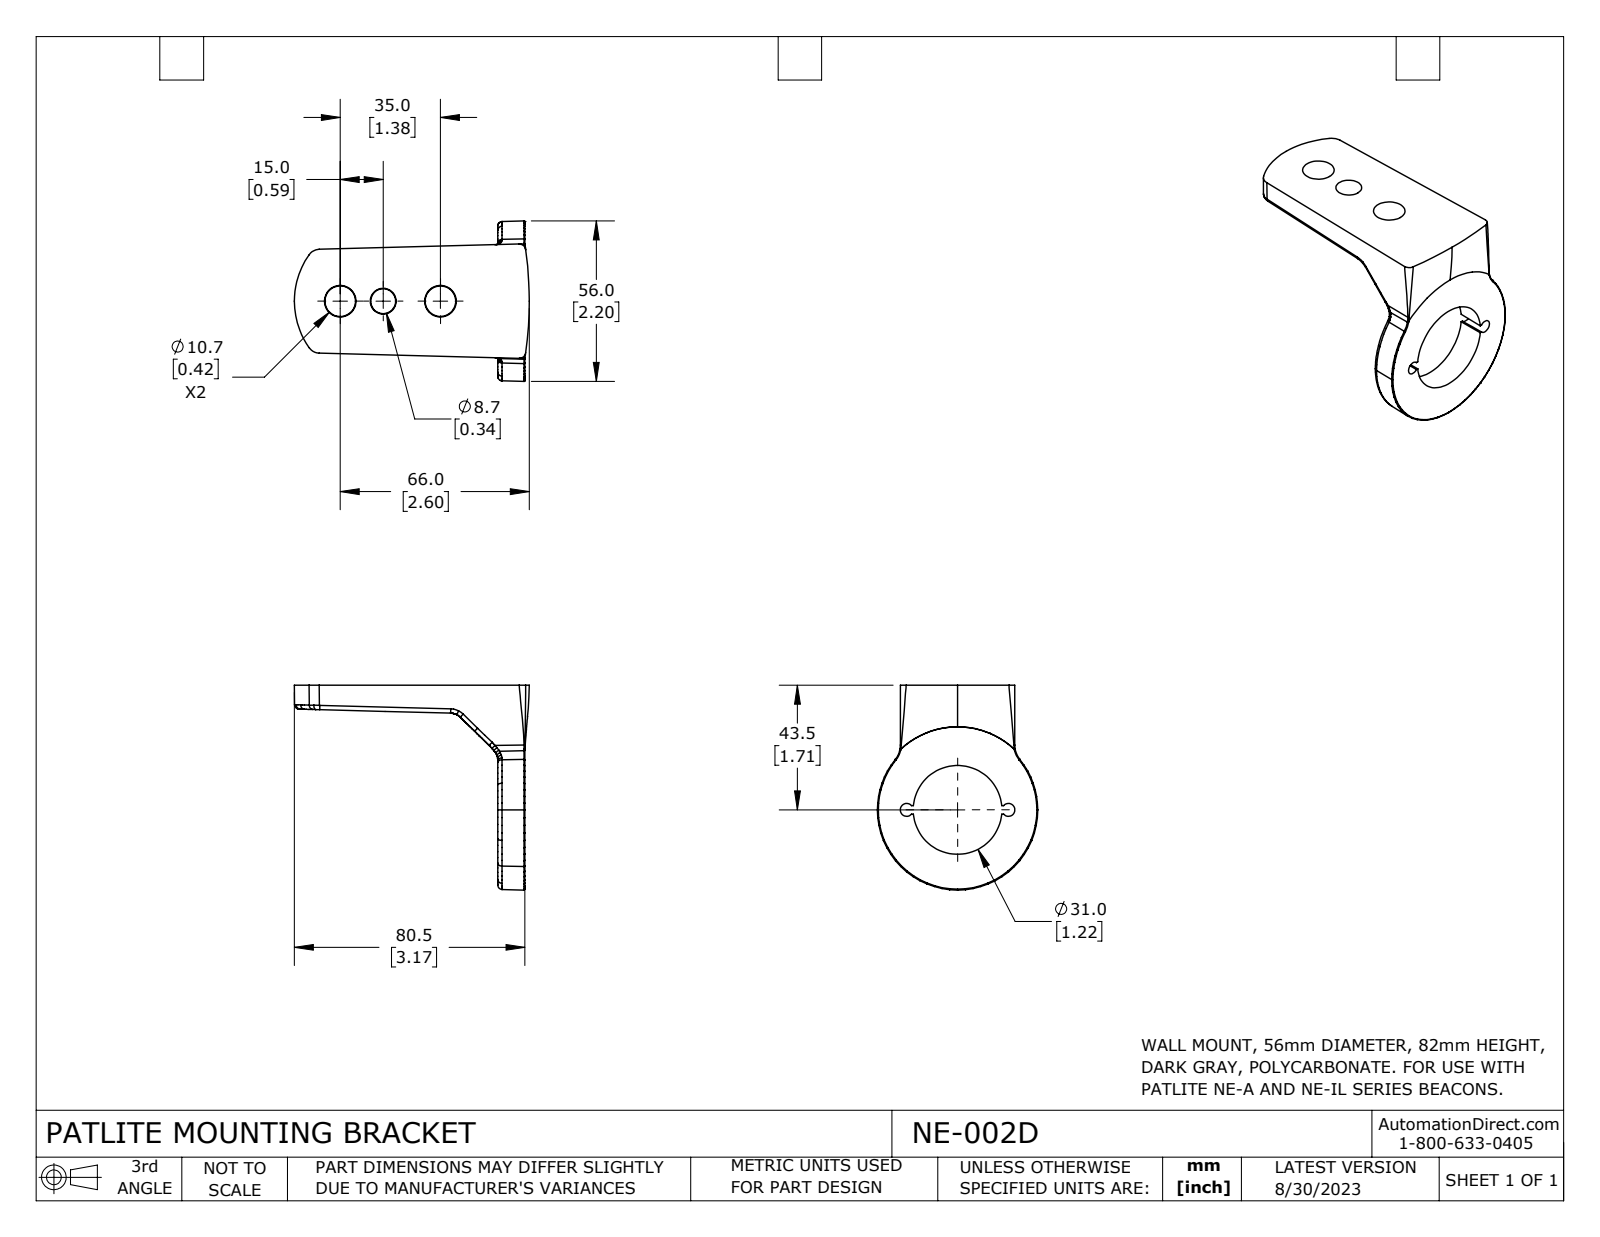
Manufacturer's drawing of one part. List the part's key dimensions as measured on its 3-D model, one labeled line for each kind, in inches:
Part name (STEP PRODUCT): NE-002D
STEP written by: SolidWorks 2021 (CONFIG_CONTROL_DESIGN)
Units: inches
Bodies: 1 solid, 240 faces (10 planar, 0 cylindrical, 230 other)
Overall size (bounding box): 3.228 × 2.815 × 2.204
Volume: 2.932 in³ · Surface area: 22.4 in²
Main face-to-face distances: 0.374
